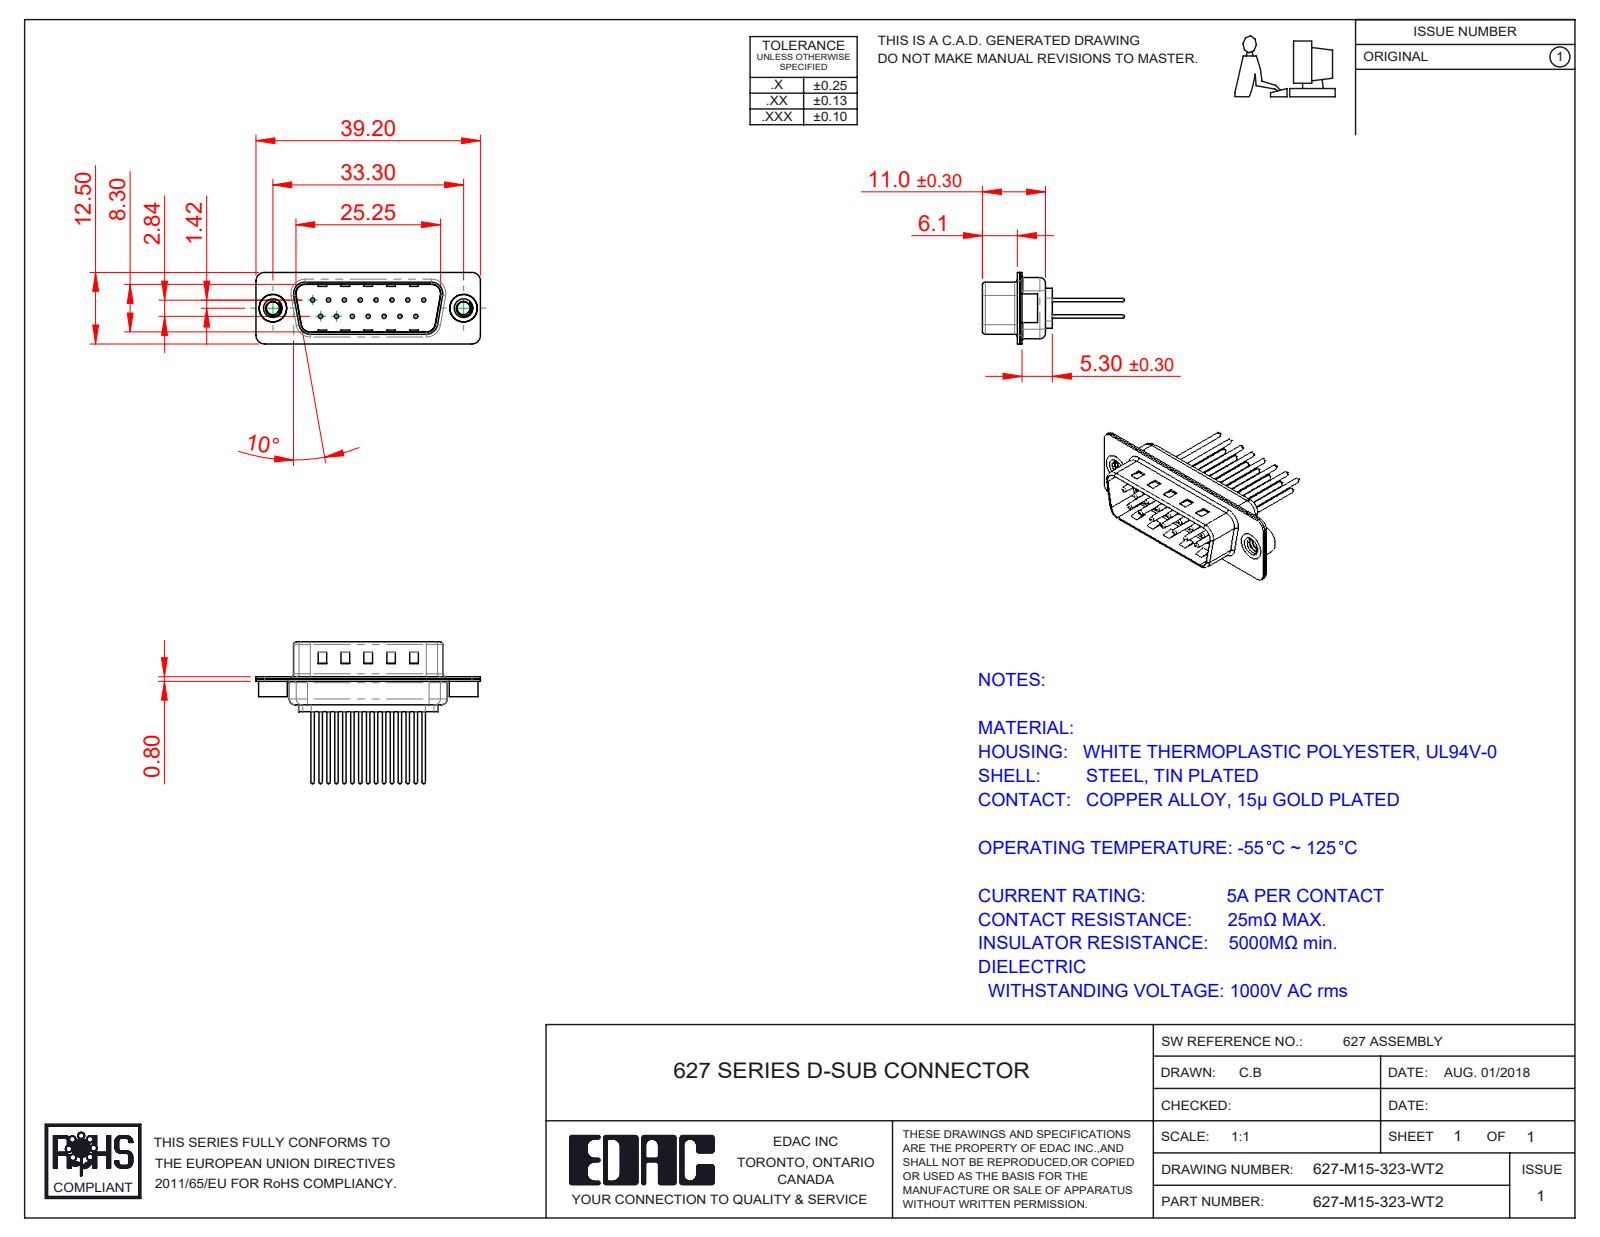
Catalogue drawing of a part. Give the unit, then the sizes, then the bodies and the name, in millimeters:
Units: millimetres
Overall size (bounding box): 39.2 × 24.77 × 12.5
Round holes (diameter × count): ⌀0.75 ×15, ⌀1.6 ×15, ⌀2 ×15, ⌀2.26 ×2, ⌀4 ×2, ⌀4.8 ×2
Round bosses / shafts (diameter × count): ⌀1.5 ×15, ⌀0.6 ×15, ⌀5 ×2, ⌀4.9 ×2
Partial cylindrical surfaces — rounded edges, fillets, slot ends (radius × count): R1.5 ×16, R2 ×12, R0.5 ×8, R1.6 ×8, R0.25 ×4, R0.6 ×4, R0.65 ×4, R0.9 ×4
Main face-to-face distances: 0.4, 0.8, 9.5, 9.1, 8.7, 9.9, 1.2, 6.1, 5.3, 5.7
Hole centre spacings: 3.16, 2.77, 5.54, 8.31, 11.08, 5.03, 5.04, 7.48
Volume: 1 873 mm³ · Surface area: 5 003 mm²
Bodies: 20 solids, 895 faces (244 planar, 343 cylindrical, 308 other)
Part name (STEP PRODUCT): 627M Contact Row 1_23; 627M Shell Front_15 Contacts; 627M Shell Rear_15 Contacts; 627-M15-323-WT2 (+3 more)
STEP written by: SolidWorks 2020 (CONFIG_CONTROL_DESIGN)
